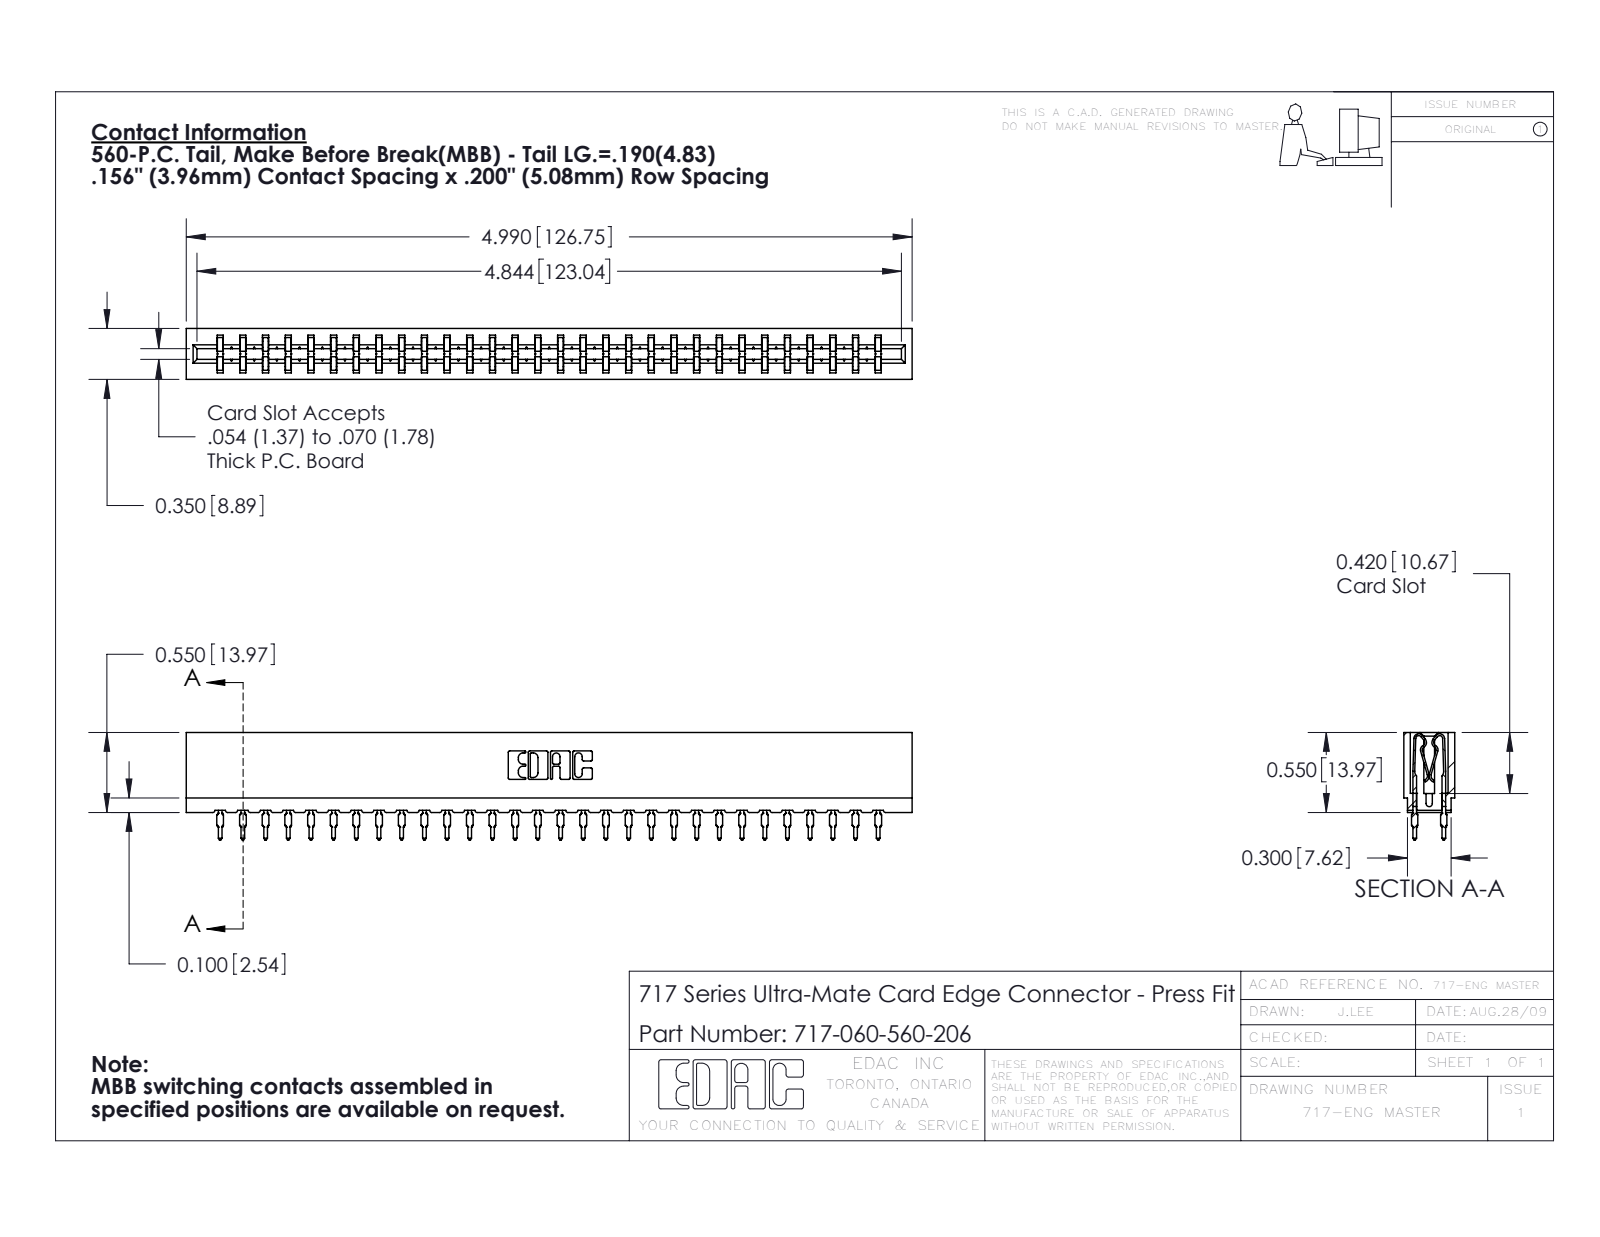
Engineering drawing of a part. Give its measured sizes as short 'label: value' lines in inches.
name: 717-060-560-206; 745-292-001_560; 717 Part_Insulator Option - 06
written by: SolidWorks 2016 (CONFIG_CONTROL_DESIGN)
unit: in
bodies: 61 solids, 6034 faces (3144 planar, 1330 cylindrical, 1560 other)
size: 4.99 × 0.739 × 0.35
volume: 0.687 in³; area: 28.07 in²
rounds: 120× R0.021, 60× R0.015, 22× R0.01, 8× R0.005, 8× R0.011, 6× R0.007, 6× R0.031, 3× R0.026
face distances: 0.212, 0.138, 0.35, 0.063, 0.287, 0.076, 0.149, 0.074, 0.156, 0.045
